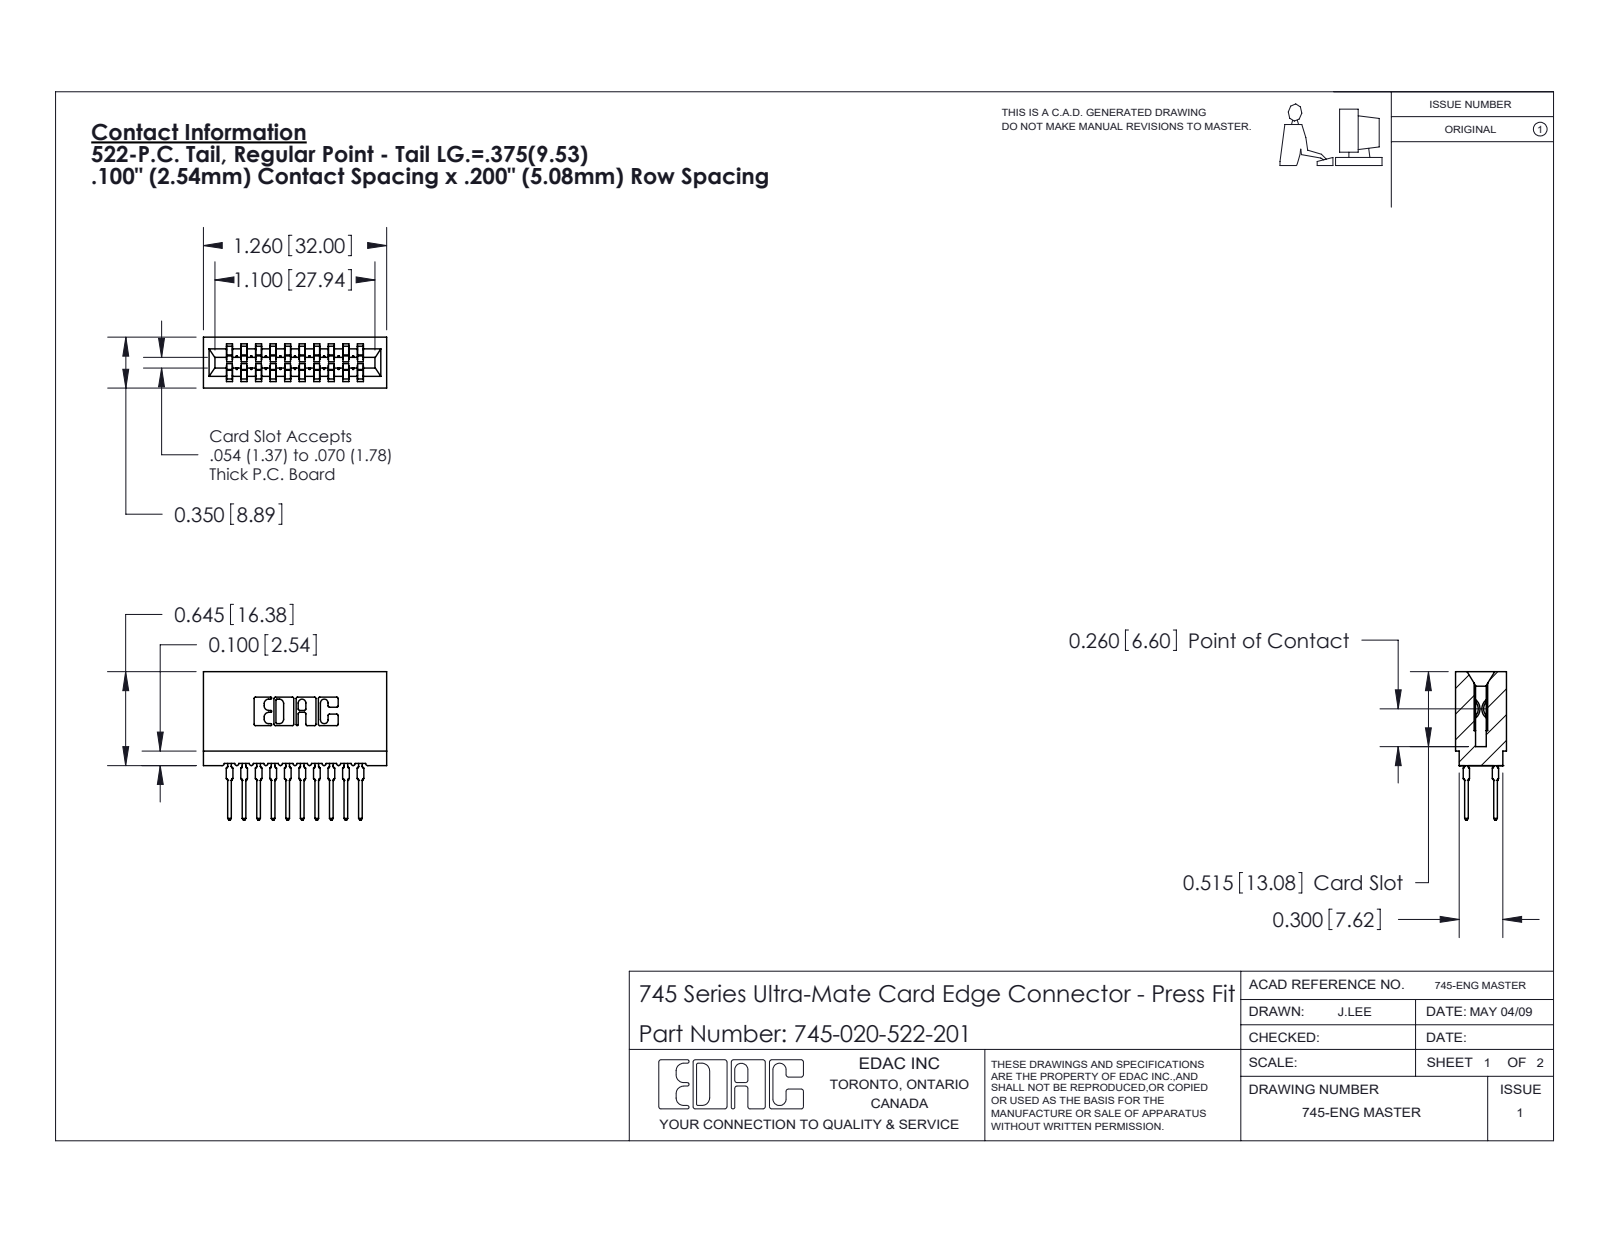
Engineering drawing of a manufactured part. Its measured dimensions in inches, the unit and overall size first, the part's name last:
Units: inches
Overall size (bounding box): 1.26 × 1.021 × 0.35
Partial cylindrical surfaces — rounded edges, fillets, slot ends (radius × count): R0.021 ×40, R0.01 ×22, R0.015 ×20, R0.005 ×8, R0.011 ×8, R0.007 ×6, R0.031 ×6, R0.026 ×3
Main face-to-face distances: 0.2, 0.1, 0.3, 0.4, 0.5, 0.158, 0.058, 0.042, 0.258, 0.142
Volume: 0.189 in³ · Surface area: 8.718 in²
Bodies: 21 solids, 1885 faces (975 planar, 390 cylindrical, 520 other)
Part name (STEP PRODUCT): 745 Part_Insulator Option - 01; 745-020-522-201; 745-292-001_522
STEP written by: SolidWorks 2020 (CONFIG_CONTROL_DESIGN)
